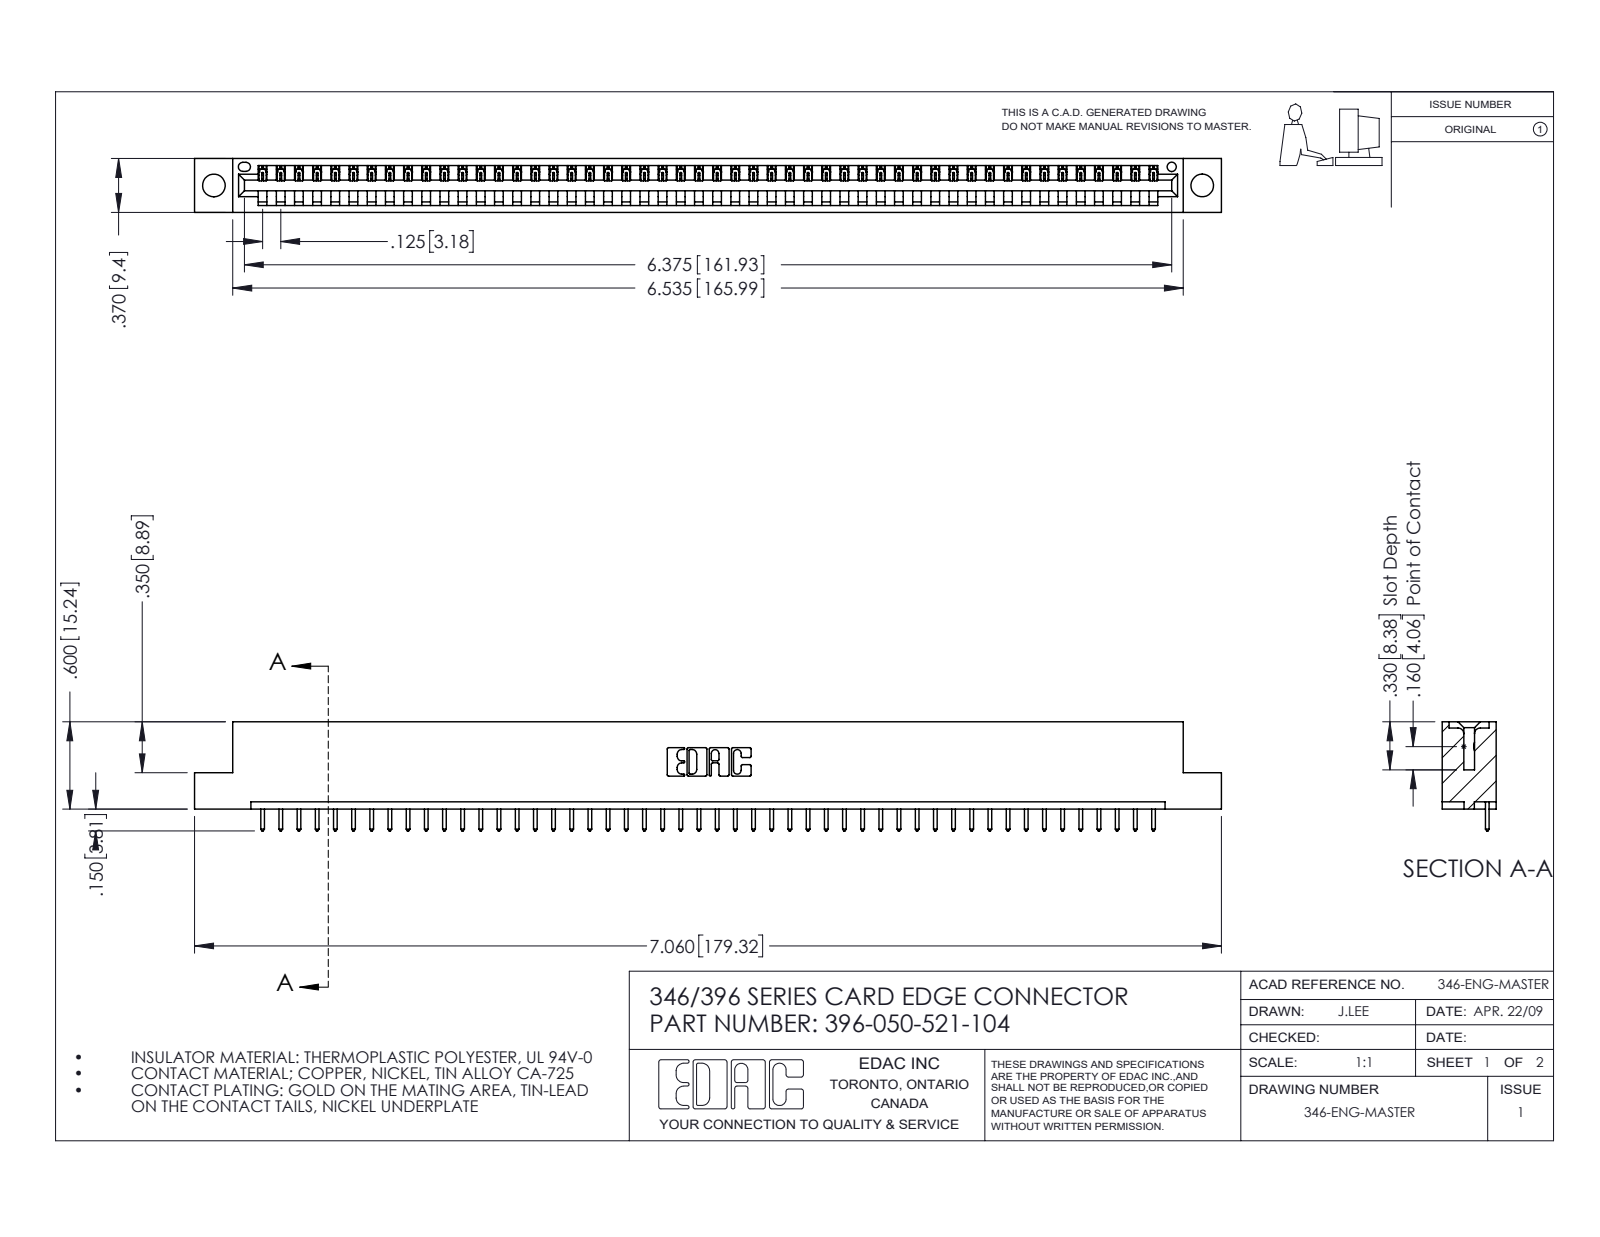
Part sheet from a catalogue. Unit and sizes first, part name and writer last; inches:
Units: inches
Overall size (bounding box): 7.06 × 0.75 × 0.37
Round holes (diameter × count): ⌀0.156 ×2, ⌀0.064 ×1
Partial cylindrical surfaces — rounded edges, fillets, slot ends (radius × count): R0.006 ×100, R0.01 ×100, R0.01 ×22, R0.007 ×6, R0.031 ×6, R0.026 ×3, R0.031 ×2, R0.04 ×2
Main face-to-face distances: 0.048, 0.322, 0.37, 0.25, 0.072, 0.298, 0.025, 0.148, 0.222, 0.1
Hole centre spacings: 0.246, 6.586, 6.795
Volume: 1.037 in³ · Surface area: 31.87 in²
Bodies: 51 solids, 3022 faces (2076 planar, 946 cylindrical, 0 other)
Part name (STEP PRODUCT): 346 Part_Flush Mounting Lugs - 0.156 Dia-TH; 345-292-001_345-293-121; 396-050-521-104
STEP written by: SolidWorks 2016 (CONFIG_CONTROL_DESIGN)
